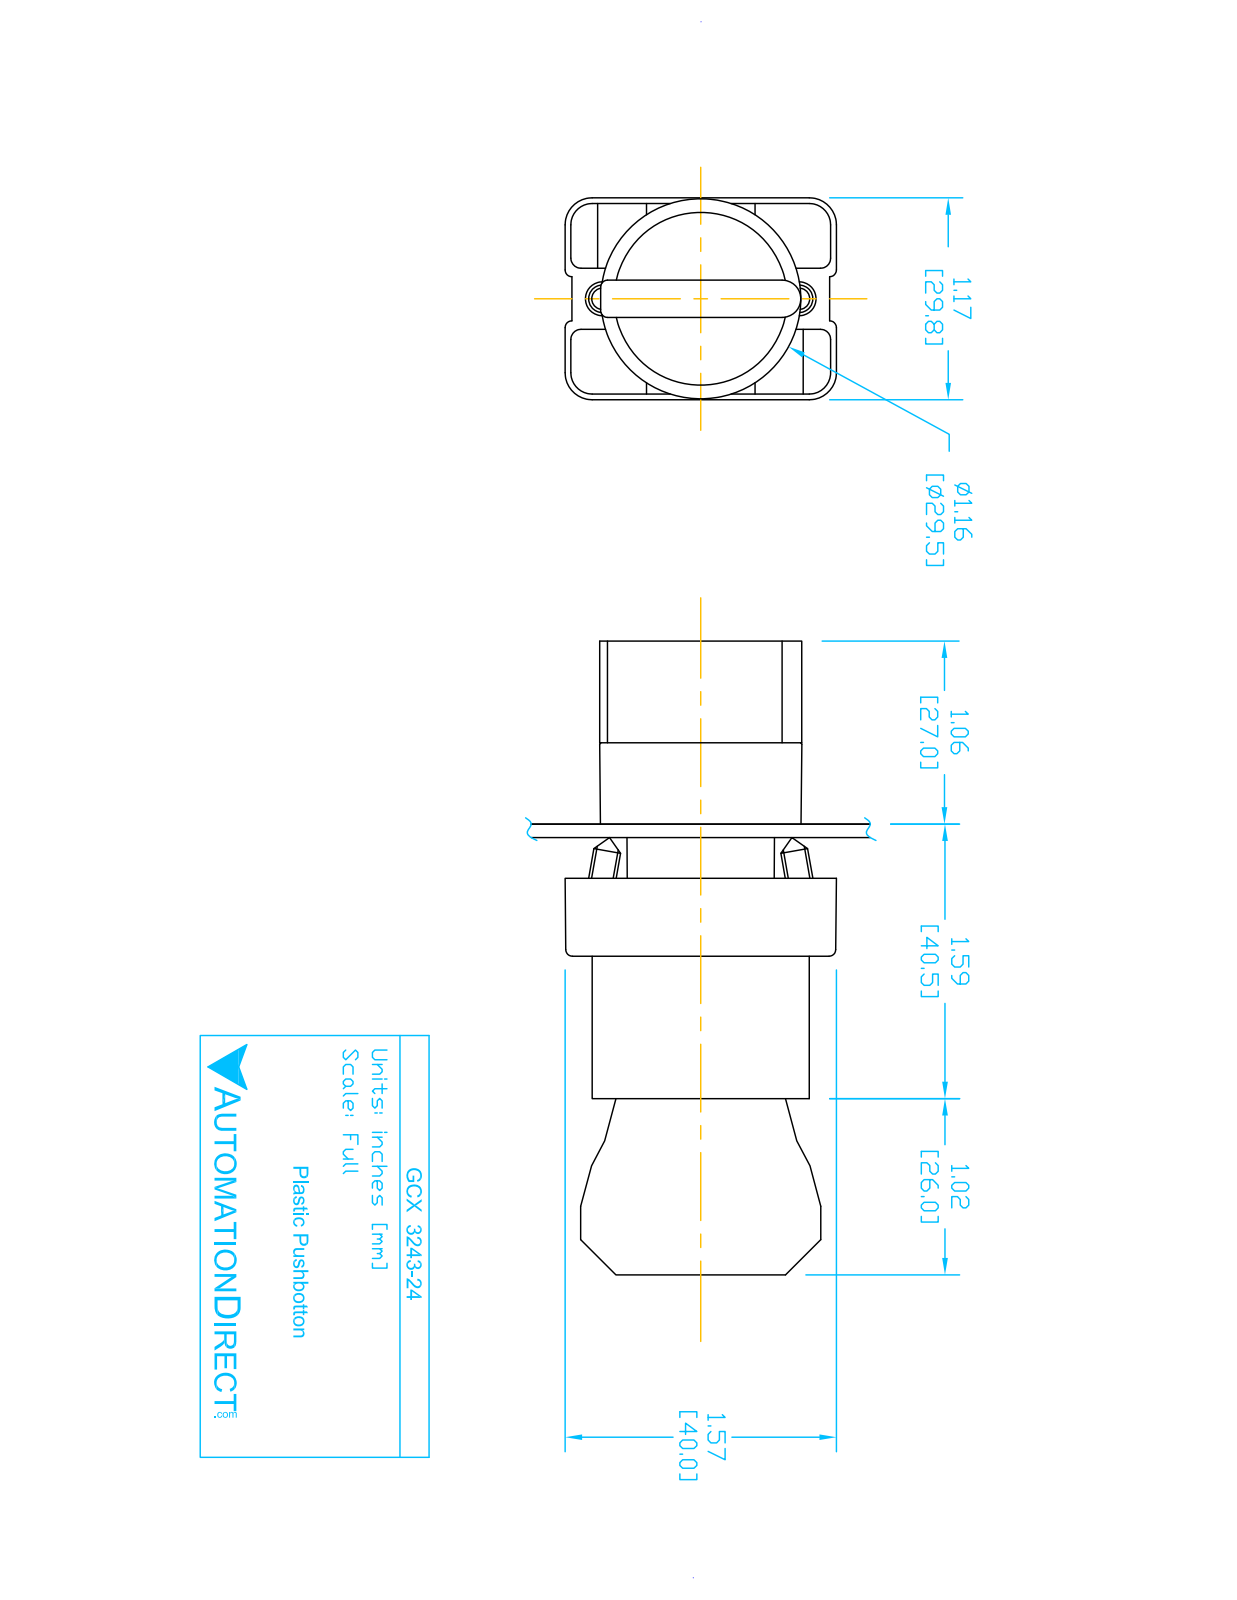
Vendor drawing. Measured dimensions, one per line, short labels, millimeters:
name: ecx1040; ECX1050; GCX3243 OPERATOR; GCX3243-24 (+1 more)
written by: SolidWorks 2016 (AUTOMOTIVE_DESIGN)
unit: mm
bodies: 8 solids, 445 faces (263 planar, 151 cylindrical, 31 other)
size: 92.8 × 40.2 × 29.9
volume: 45 870 mm³; area: 25 160 mm²
holes: 2× ⌀2, 2× ⌀3.1, 2× ⌀3.3, 1× ⌀2.2, 1× ⌀5, 1× ⌀11.9, 1× ⌀22.3, 1× ⌀22.6, 1× ⌀26
bosses: 4× ⌀4, 1× ⌀29.8, 1× ⌀25.5, 1× ⌀24, 1× ⌀21.7, 1× ⌀19.8, 1× ⌀12.8
rounds: 24× R1.5, 12× R1, 12× R3.1, 12× R4, 9× R1, 2× R3.3, 1× R0.5, 1× R1.6
face distances: 21, 51.3, 30.3, 14.7, 31.6, 29.7, 12, 11.9, 0.8, 0.8
hole spacings: 6, 13.8, 12, 12.4
